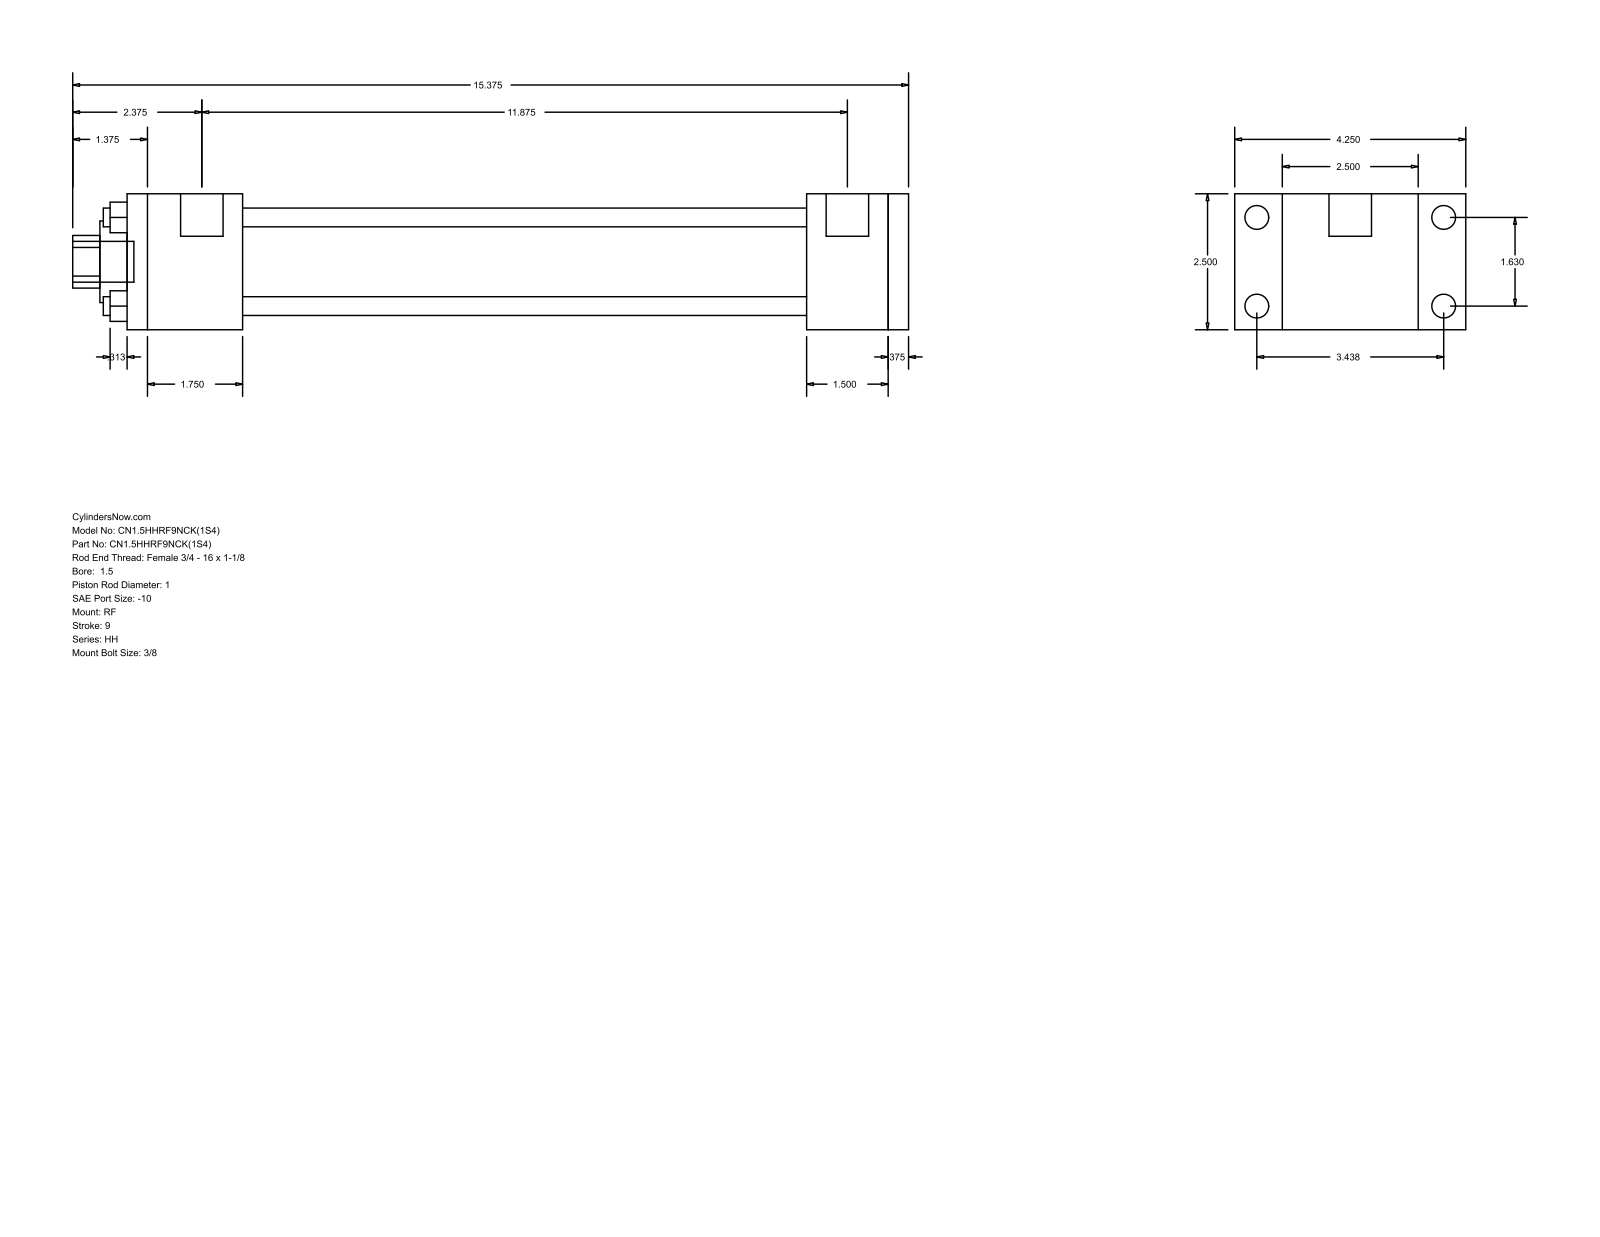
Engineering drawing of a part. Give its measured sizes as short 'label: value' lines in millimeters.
name: HH_RF__0150_1
written by: GSSL Pune (CONFIG_CONTROL_DESIGN)
unit: mm
bodies: 0 solids, 92 faces (64 planar, 28 cylindrical, 0 other)
size: 390.52 × 107.95 × 63.5
holes: 4× ⌀8.76, 1× ⌀25.4, 1× ⌀38.1, 1× ⌀44.45
bosses: 4× ⌀11.13, 4× ⌀5.56, 2× ⌀19.84, 1× ⌀19.05
rounds: 1× R12.29
face distances: 63.5, 9.52, 263.52, 301.62, 311.14, 38.1, 47.62, 53.98, 317.5, 355.6
hole spacings: 29.27, 41.4, 58.55
